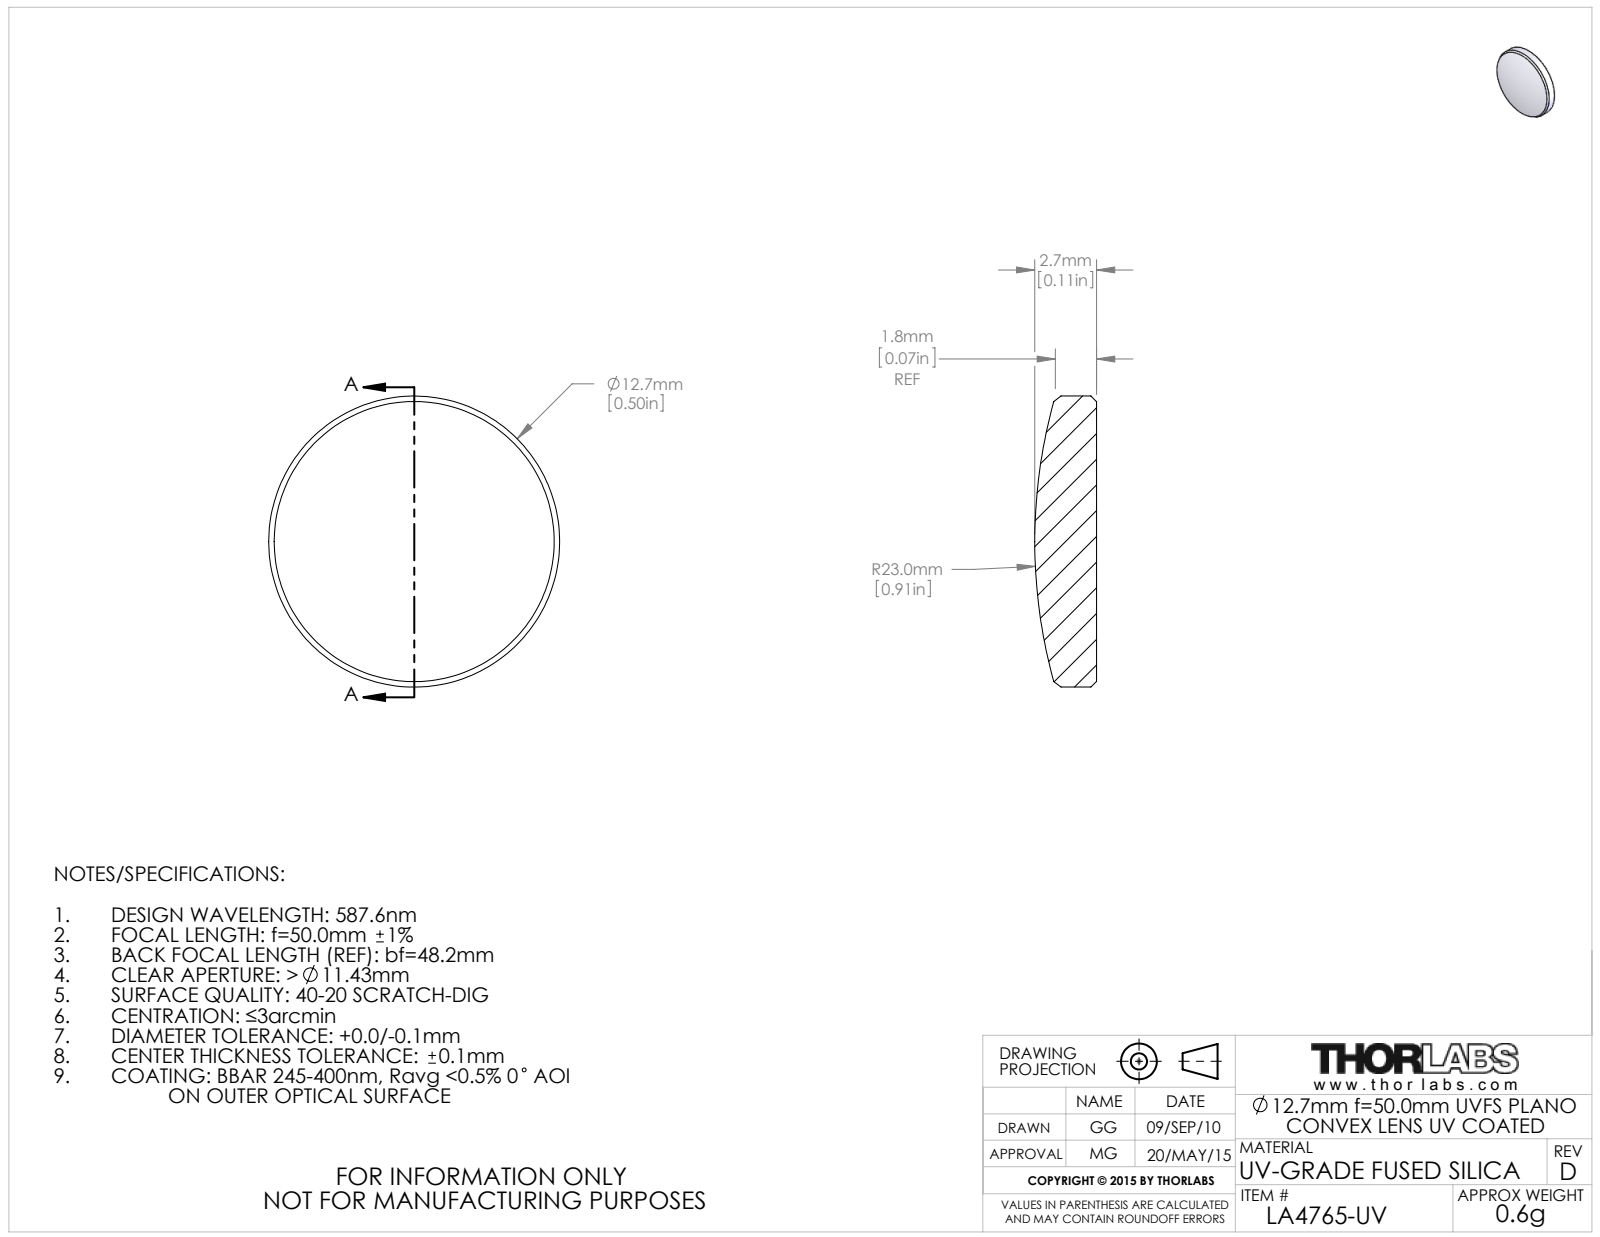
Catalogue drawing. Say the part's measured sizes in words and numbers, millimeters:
The part is named "4275-E0W". Its 3-D file was written by "SolidWorks 2014 (CONFIG_CONTROL_DESIGN)". It is 1 solid with 9 faces: 1 planar, 2 cylindrical and 6 other. Overall it measures 12.7 by 12.7 by 2.7 millimeters. Its volume is 283 cubic millimeters and its surface area 318 square millimeters. Round bosses or shafts: 1 of diameter 12.7.
